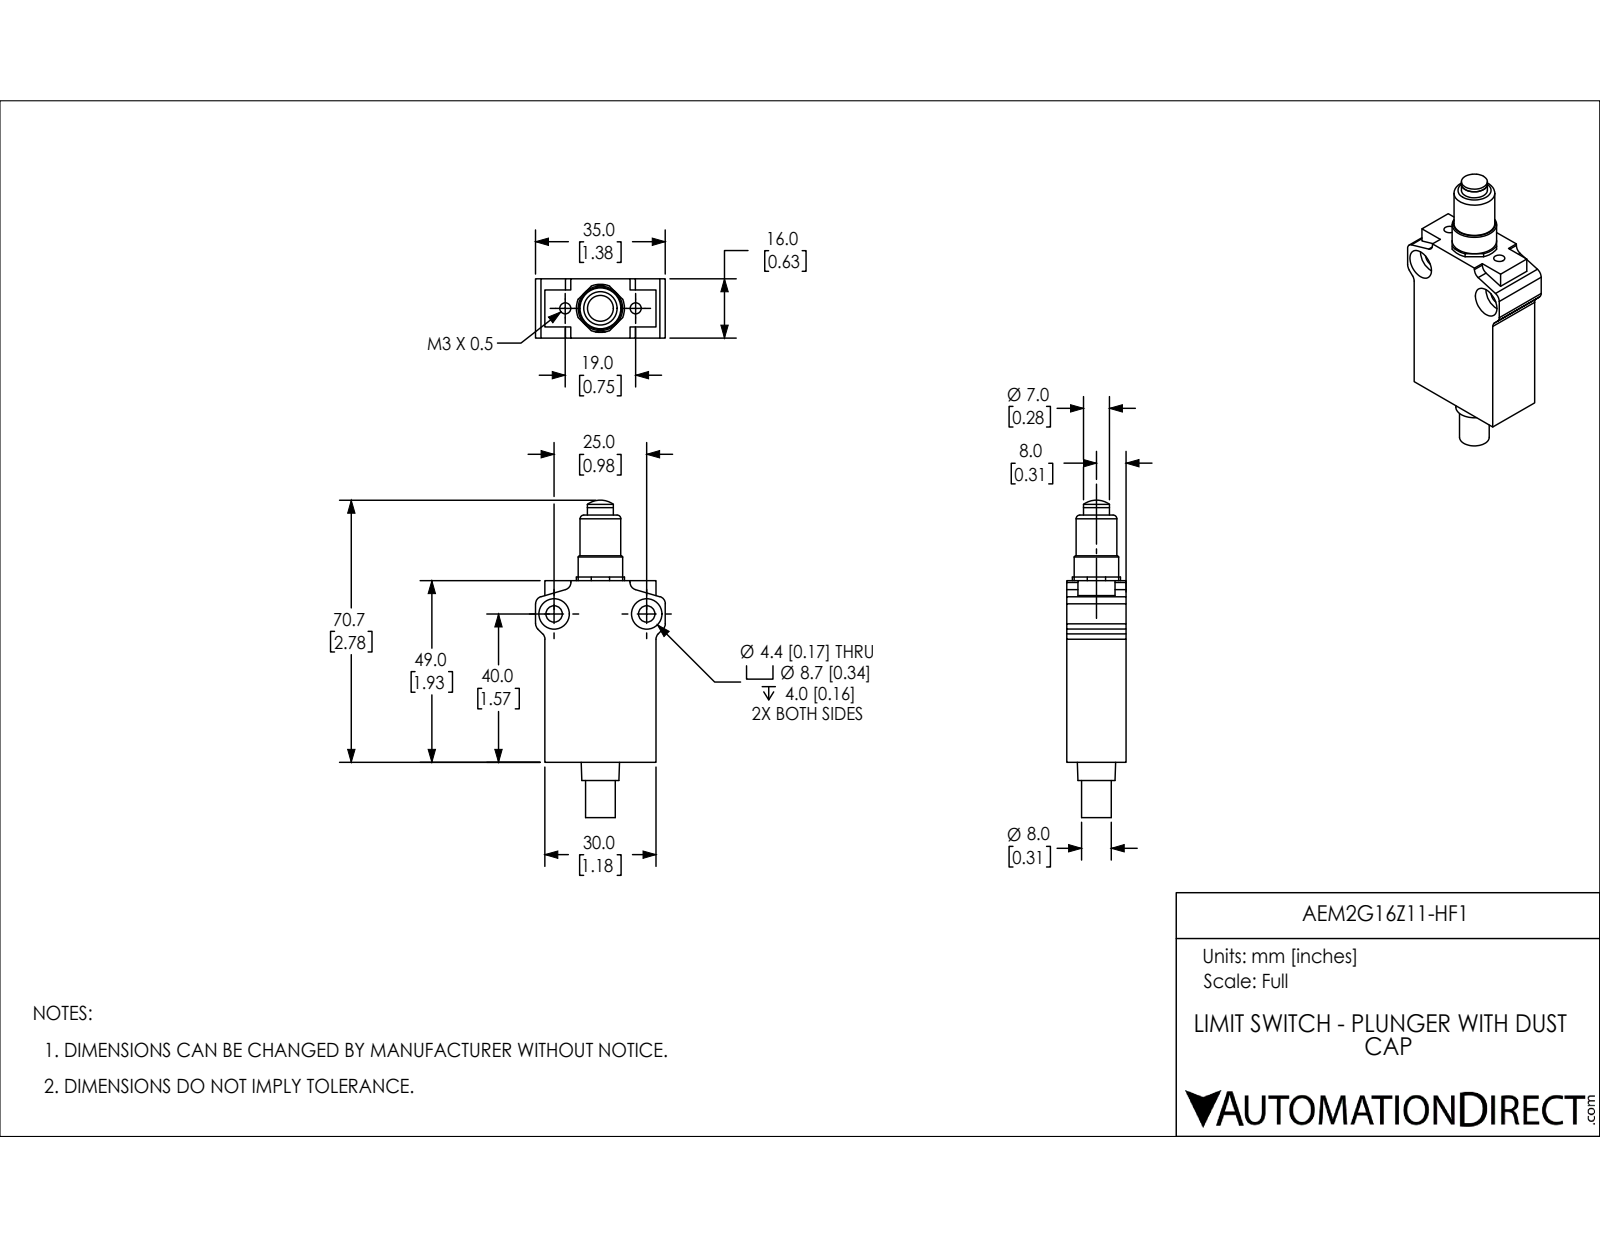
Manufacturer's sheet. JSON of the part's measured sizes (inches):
{"part_name": "AEM2G16Z11-HF1", "step_written_by": "SolidWorks 2018 (AUTOMOTIVE_DESIGN)", "units": "inches", "bodies": {"solids": 3, "faces": 133, "planar": 54, "cylindrical": 67, "other": 12}, "overall_size": [3.37, 1.378, 0.63], "volume_in3": 1.547, "surface_area_in2": 13.86, "round_holes": [[0.118, 2], [0.173, 2], [0.323, 2], [0.197, 1], [0.28, 1]], "round_bosses_or_shafts": [[0.472, 1], [0.433, 1], [0.315, 1], [0.276, 1]], "partial_cylinders_radius": [[0.079, 8], [0.256, 1]], "face_to_face_distances": [0.63, 1.181, 1.929, 0.039, 0.472, 0.098, 1.28, 0.157, 0.189, 0.15], "hole_center_spacings": [0.374, 0.748, 0.984]}
